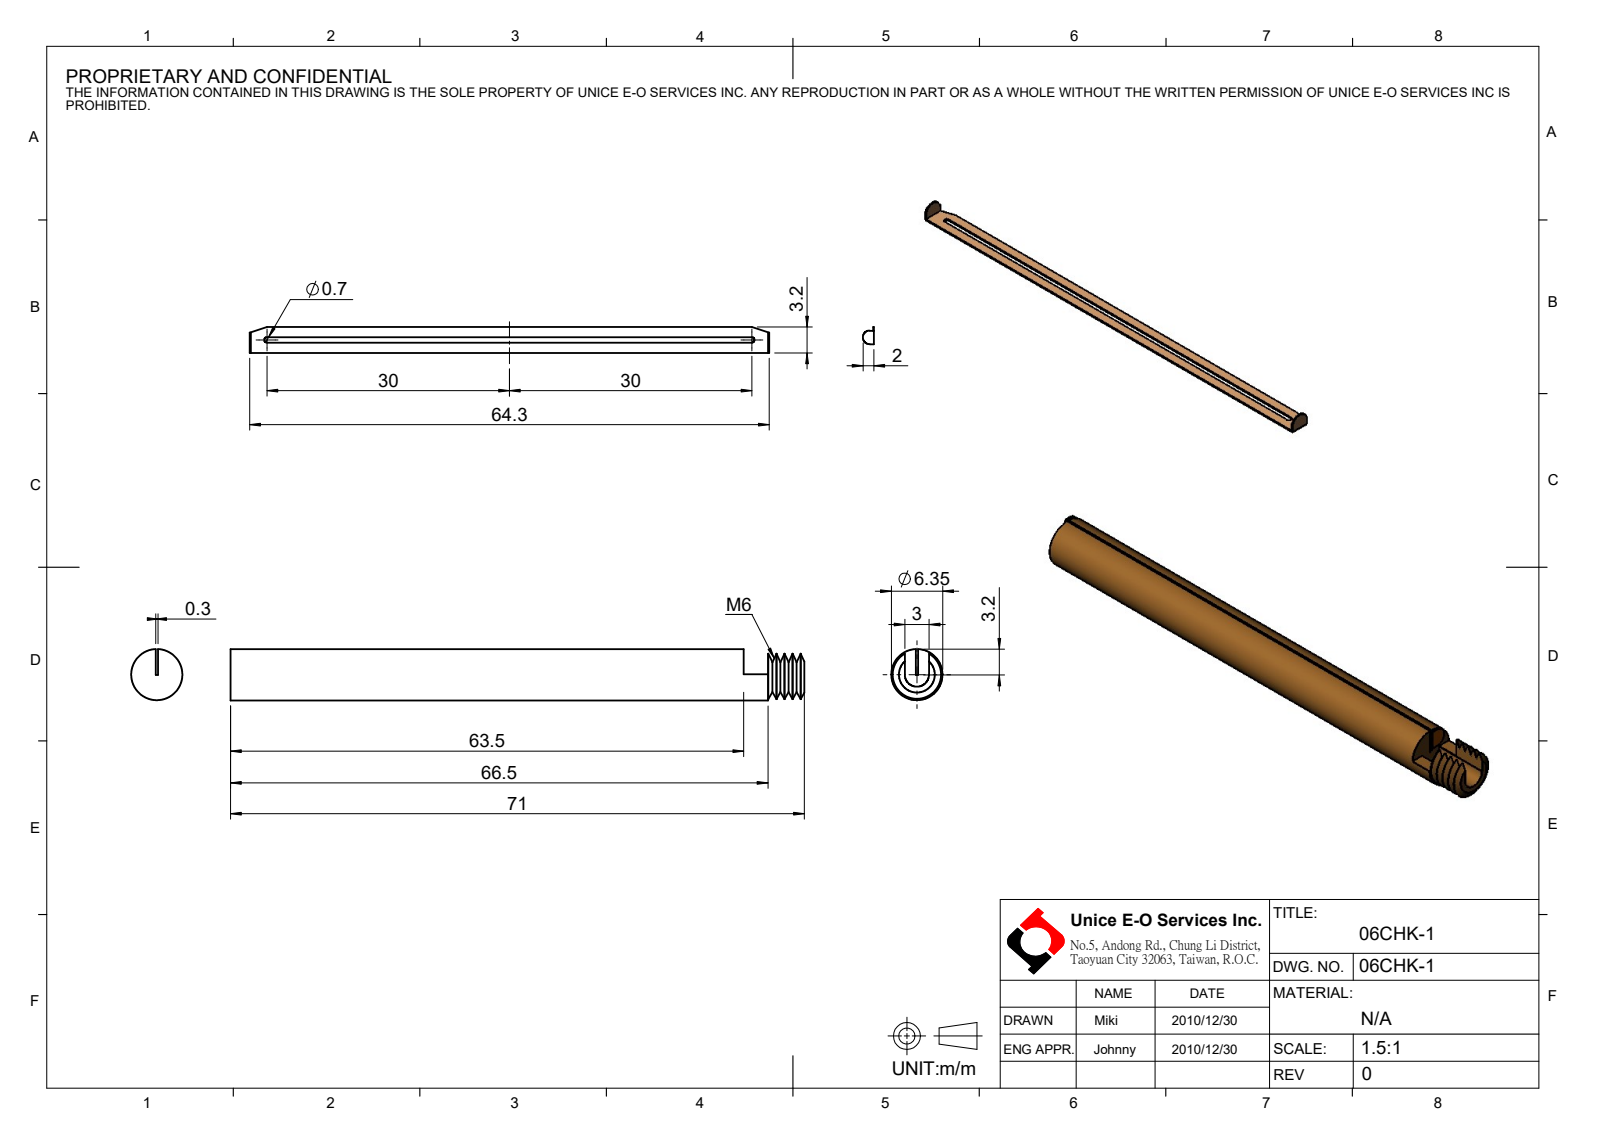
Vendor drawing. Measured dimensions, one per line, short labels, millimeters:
name: 06CHK-1
written by: SolidWorks 2016 (CONFIG_CONTROL_DESIGN)
unit: mm
bodies: 2 solids, 77 faces (27 planar, 23 cylindrical, 27 other)
size: 71.4 × 6.35 × 6.35
volume: 2 060 mm³; area: 2 324 mm²
bosses: 1× ⌀6.35, 1× ⌀6
rounds: 2× R0.35, 1× R1.25, 1× R1.5
face distances: 1.35, 1.65, 1.25, 63.5, 1.95, 3, 3.2, 3.1, 1.42, 1.57
